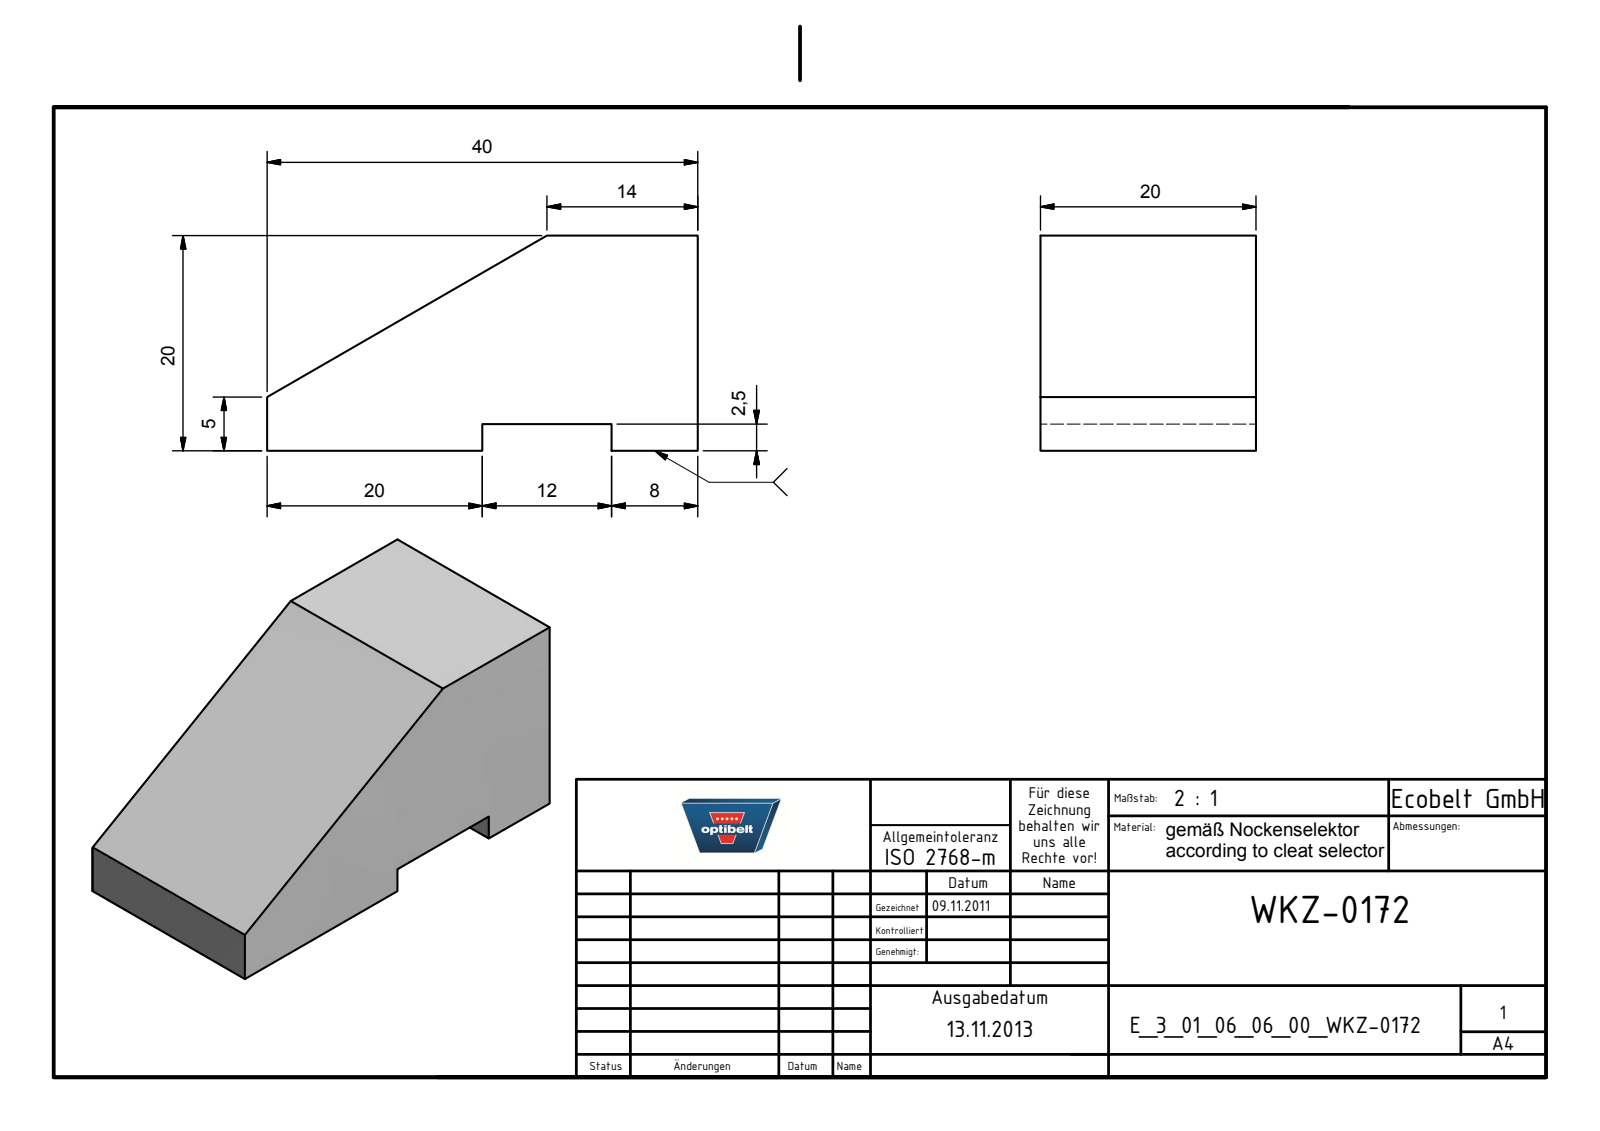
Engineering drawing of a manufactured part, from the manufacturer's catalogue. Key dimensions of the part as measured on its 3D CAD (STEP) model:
Part name (STEP PRODUCT): E_3_01_06_06_00_WKZ-0172
STEP written by: Autodesk Inventor 2025 (AUTOMOTIVE_DESIGN)
Units: millimetres
Bodies: 1 solid, 11 faces (11 planar, 0 cylindrical, 0 other)
Overall size (bounding box): 40 × 20 × 20
Volume: 11 500 mm³ · Surface area: 3 430 mm²
Main face-to-face distances: 20, 2.5, 17.5, 40, 32, 8, 12
